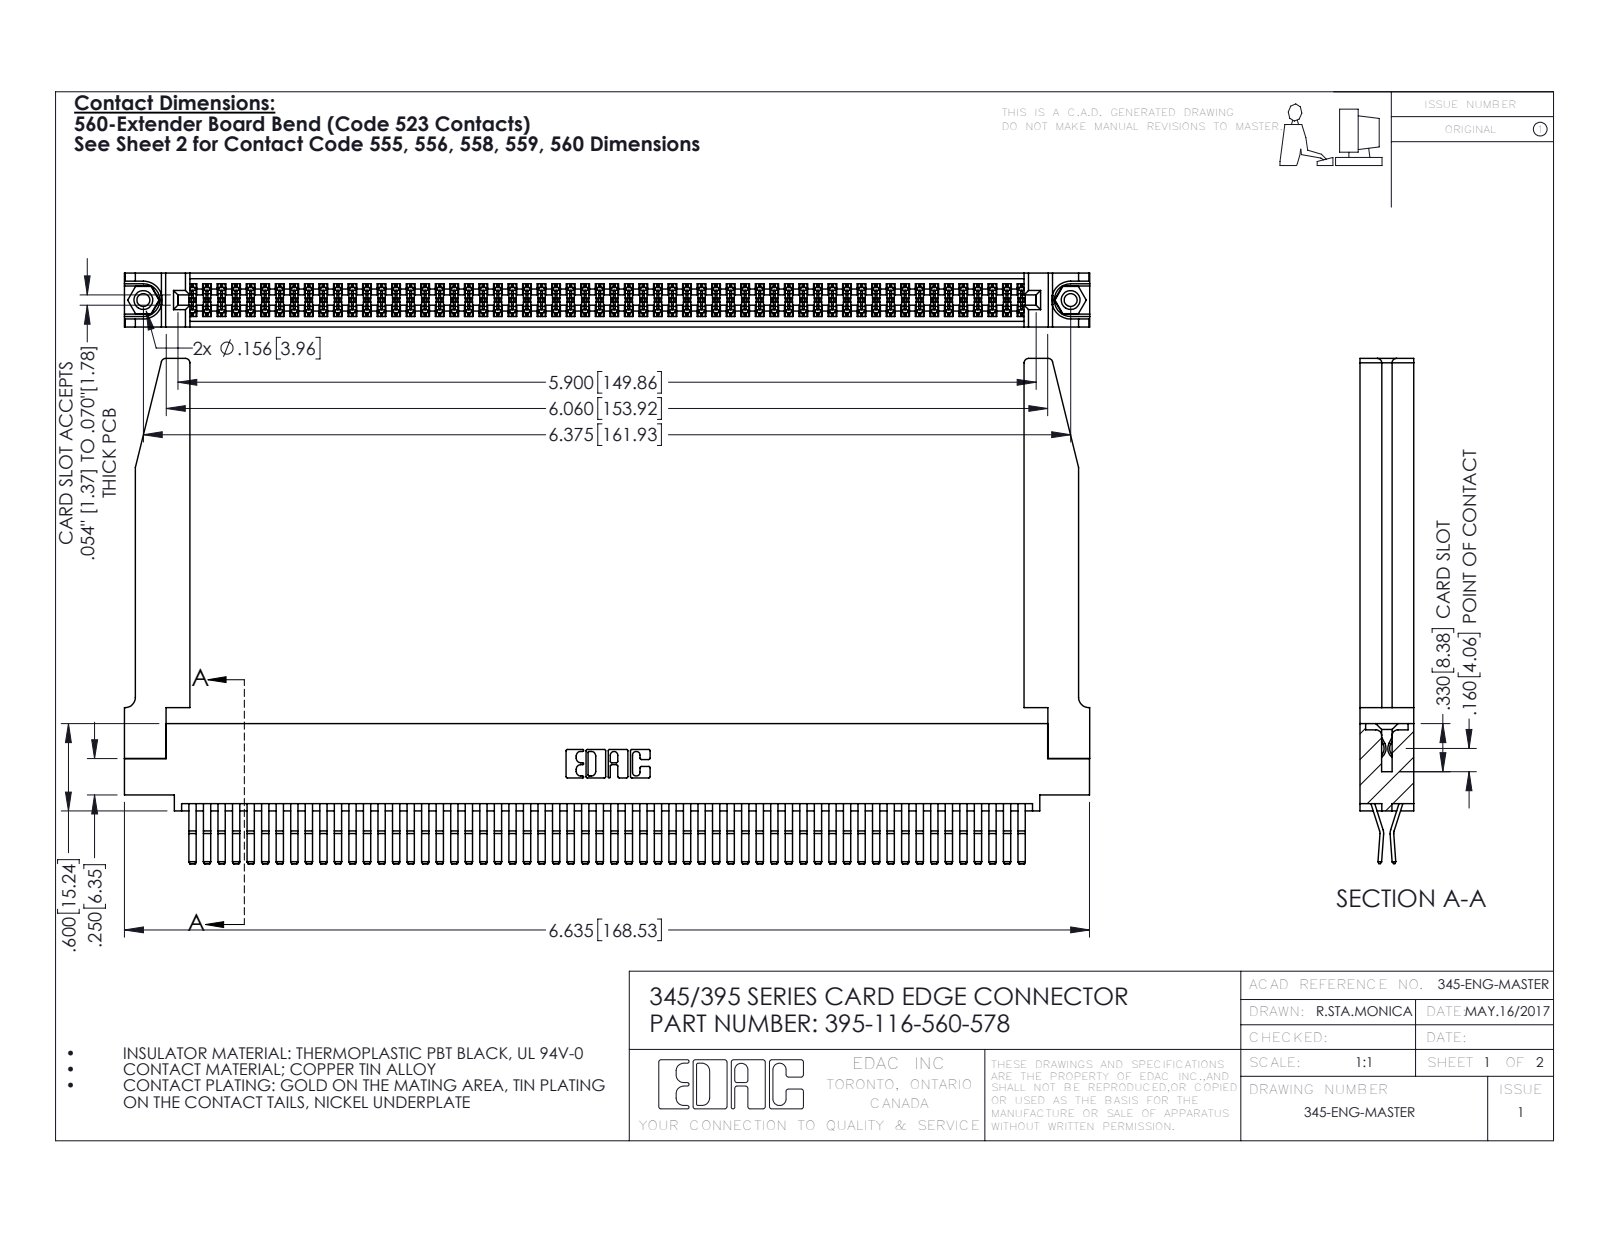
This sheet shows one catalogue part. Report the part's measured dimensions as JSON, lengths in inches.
{"part_name": "395-116-560-578; 345 Part_0.110 Offset - 0.156 Dia-TH; 345-292-001_560 Tail; 345-220-078_345-220-078 (+1 more)", "step_written_by": "SolidWorks 2016 (CONFIG_CONTROL_DESIGN)", "units": "inches", "bodies": {"solids": 121, "faces": 6396, "planar": 4054, "cylindrical": 2290, "other": 52}, "overall_size": [6.636, 3.472, 0.37], "volume_in3": 1.524, "surface_area_in2": 53.68, "round_holes": [[0.089, 2], [0.125, 2], [0.156, 2], [0.064, 1]], "round_bosses_or_shafts": [[0.155, 2]], "partial_cylinders_radius": [[0.006, 175], [0.01, 22], [0.03, 8], [0.007, 6], [0.031, 6], [0.026, 3], [0.01, 2], [0.014, 2]], "face_to_face_distances": [0.072, 0.37, 0.298, 0.025, 0.2, 0.098, 0.272, 0.225, 0.175, 0.15], "hole_center_spacings": [0.27, 6.139, 6.375]}
